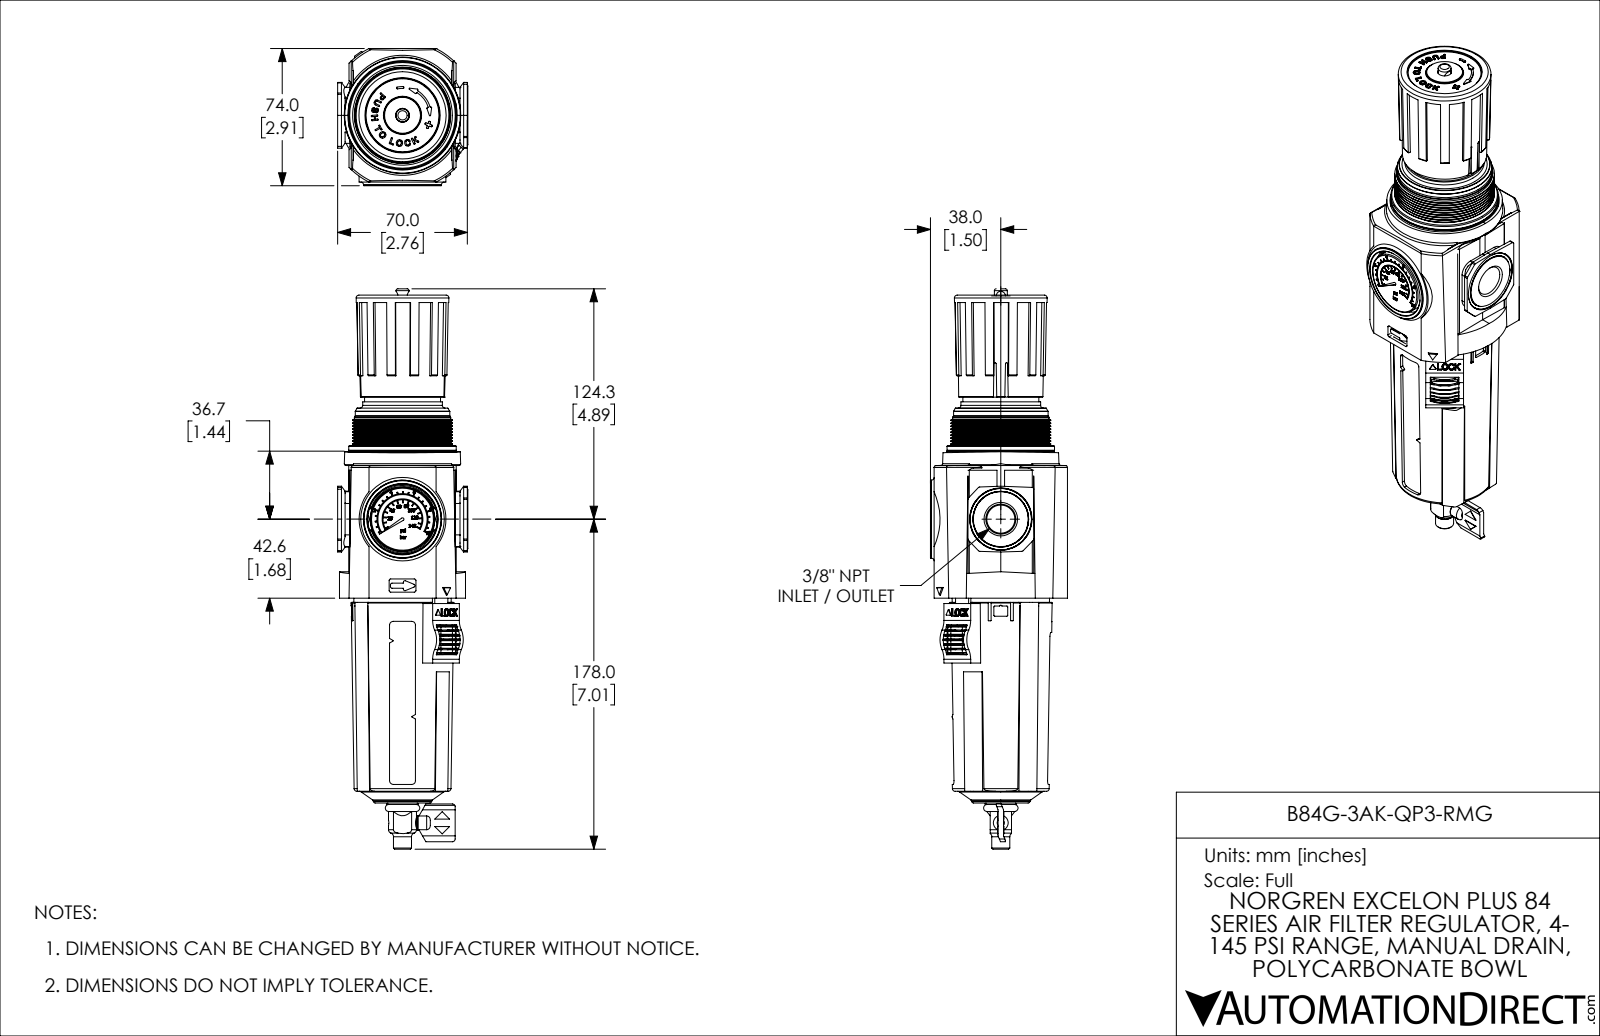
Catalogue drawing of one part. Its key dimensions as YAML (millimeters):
part_name: "B84G-3AK-QP3-RMG"
step_written_by: "SolidWorks 2021 (CONFIG_CONTROL_DESIGN)"
units: millimeters
bodies: {solids: 8, faces: 2537, planar: 932, cylindrical: 1170, other: 435}
overall_size: [302.3, 74, 70.3]
volume: 755600
surface_area: 133600
round_holes:
  - {diameter: 4.5, count: 2}
  - {diameter: 1.5, count: 1}
  - {diameter: 3.1, count: 1}
  - {diameter: 3.2, count: 1}
  - {diameter: 5, count: 1}
  - {diameter: 6, count: 1}
  - {diameter: 6.4, count: 1}
  - {diameter: 9.5, count: 1}
  - {diameter: 24.6, count: 1}
  - {diameter: 33.5, count: 1}
  - {diameter: 59, count: 1}
  - {diameter: 62.5, count: 1}
round_bosses_or_shafts:
  - {diameter: 7.6, count: 2}
  - {diameter: 4, count: 2}
  - {diameter: 58, count: 1}
  - {diameter: 53.8, count: 1}
  - {diameter: 52, count: 1}
  - {diameter: 51.5, count: 1}
  - {diameter: 51, count: 1}
  - {diameter: 43, count: 1}
partial_cylinders:
  - {radius: 0.3, count: 27}
  - {radius: 0.5, count: 26}
  - {radius: 0.3, count: 24}
  - {radius: 1, count: 23}
  - {radius: 1.2, count: 18}
  - {radius: 0.7, count: 16}
  - {radius: 0.8, count: 16}
  - {radius: 0.1, count: 14}
face_to_face_distances: [69.1, 59, 0.9, 68.1, 15.8, 13, 53.2, 52.3, 98.2, 97.3]
hole_center_spacings: [21.7, 43.5, 284.2]
